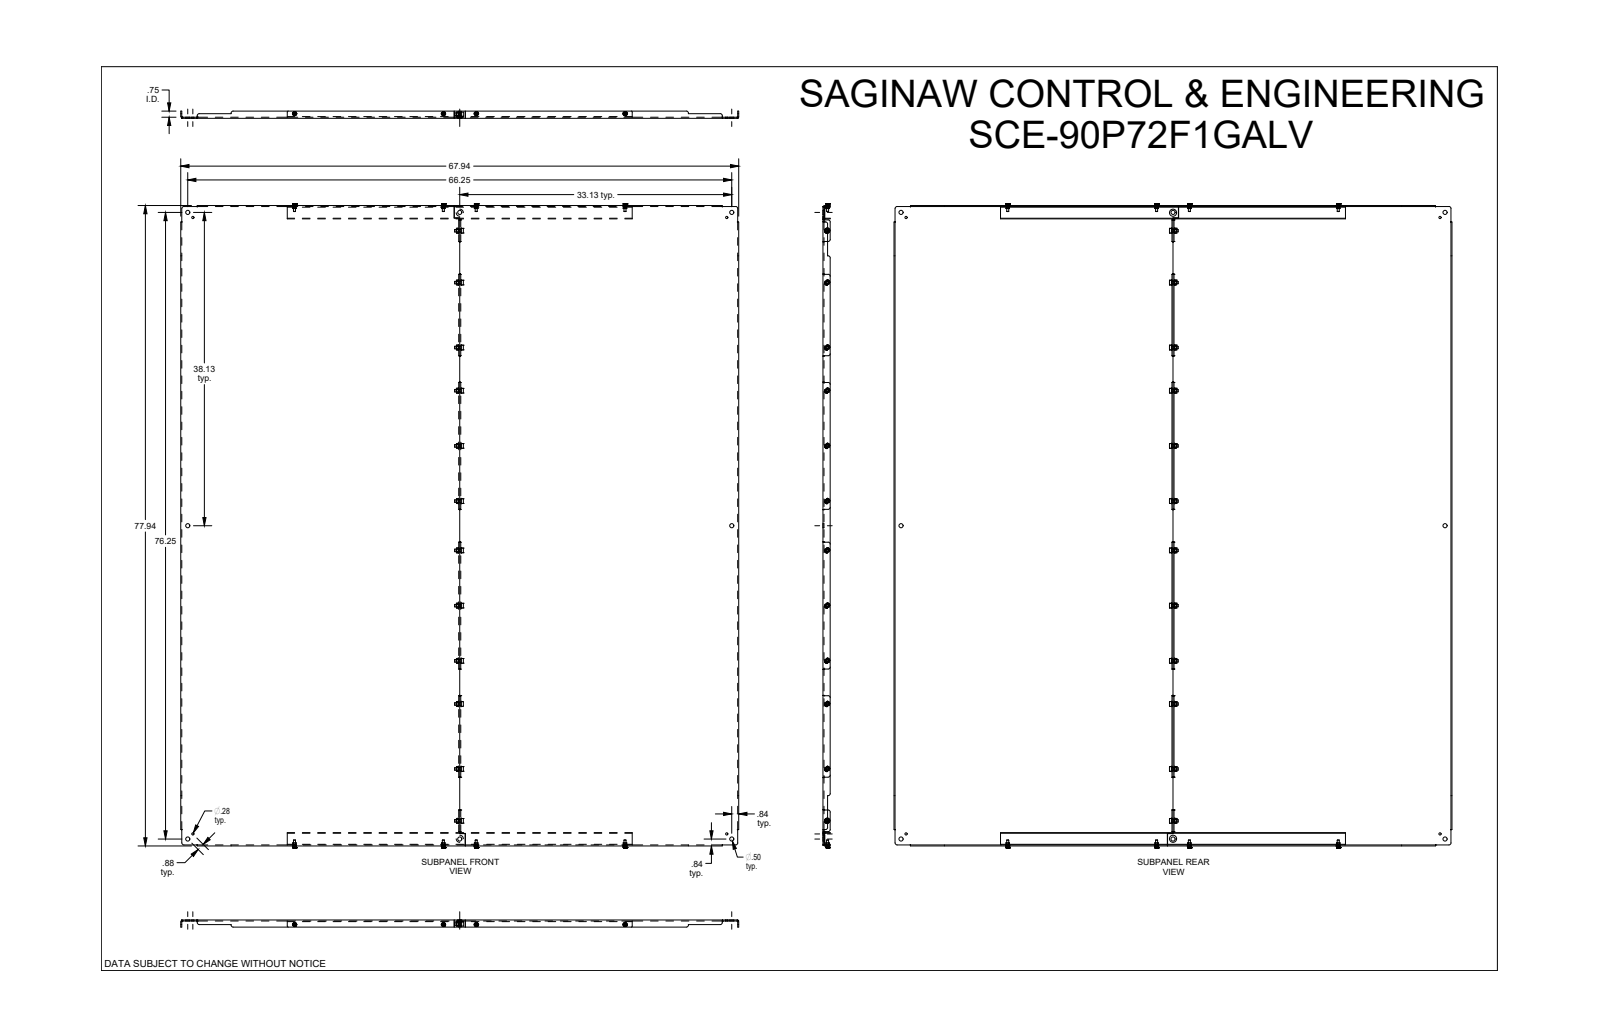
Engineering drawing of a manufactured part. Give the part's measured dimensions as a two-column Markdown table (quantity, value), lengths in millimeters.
| quantity | value |
| --- | --- |
| part name | SCE-90P72F1GALV |
| STEP written by | SolidWorks 2019 (AUTOMOTIVE_DESIGN) |
| units | millimeters |
| bodies | 44 solids, 1922 faces (528 planar, 478 cylindrical, 916 other) |
| overall size | 1991 × 1725.6 × 22.2 |
| volume | 11 680 000 mm³ |
| surface area | 7 526 000 mm² |
| round holes (diameter × count) | 7.9 × 12, 9.5 × 12, 12.7 × 8, 6.4 × 4, 7.8 × 4, 8.7 × 4, 7.1 × 3, 22.2 × 2, 7.1 × 1 |
| round bosses / shafts (diameter × count) | 7.9 × 12, 12.7 × 4, 11.2 × 4, 8.7 × 4, 6.3 × 4 |
| partial cylindrical surfaces (radius × count) | 0.3 × 200, 6.4 × 24, 1.5 × 16, 4.4 × 8, 2.8 × 6, 6 × 6, 2 × 4, 4 × 4 |
| main face-to-face distances | 3.2, 3.2, 2, 859.6, 5.2, 36.1, 1935.1, 2, 862.8, 862.8 |
| hole center spacings | 825.8, 825.8, 841.4, 841.4, 952.8, 968.4, 1921.1, 1941.5 |
